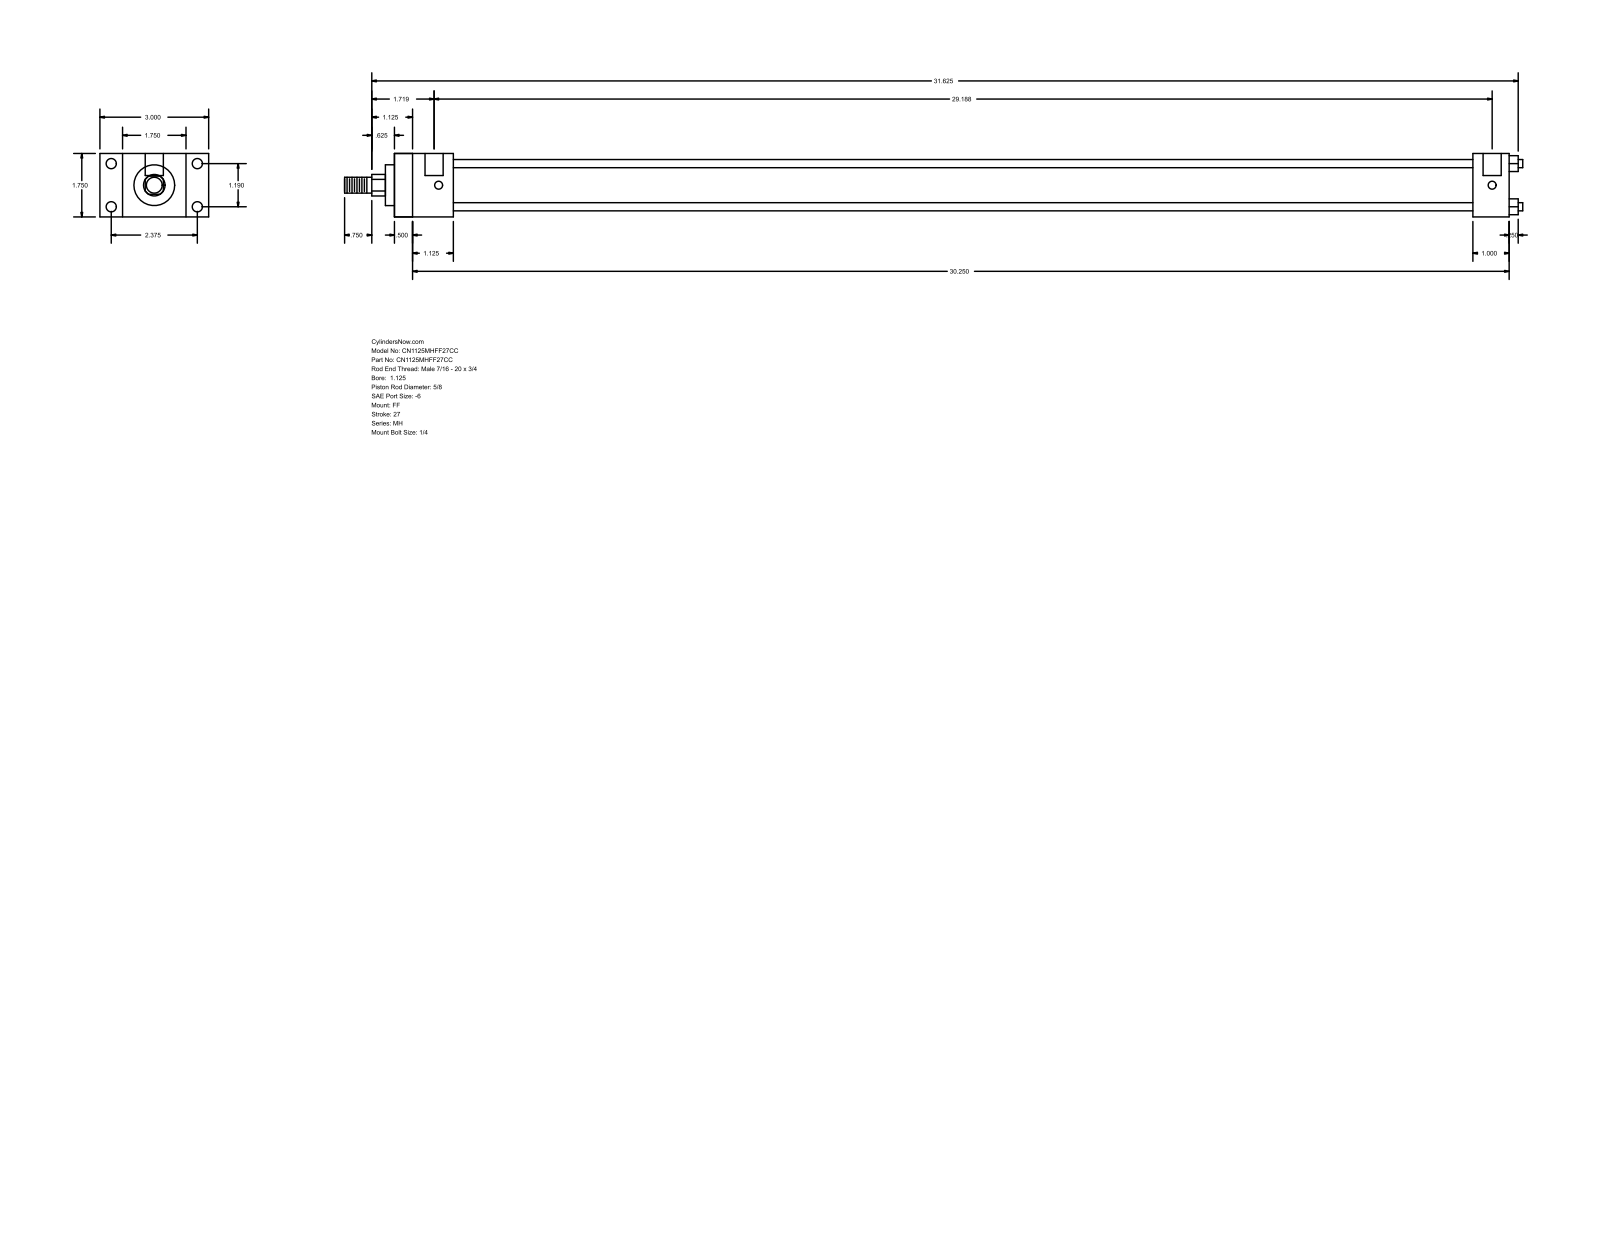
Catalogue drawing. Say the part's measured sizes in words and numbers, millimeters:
The part is named "MH_FF__0112_0.625". Its 3-D file was written by "GSSL Pune (CONFIG_CONTROL_DESIGN)". It is 0 solids with 92 faces: 64 planar, 28 cylindrical and 0 other. Overall it measures 825.5 by 76.2 by 44.45 millimeters. Round holes: 4 of diameter 5.56, 4 of diameter 7.14, 2 of diameter 12.7. Round bosses or shafts: 4 of diameter 5.71, 1 of diameter 34.92, 1 of diameter 28.57, 1 of diameter 15.88, 1 of diameter 11.11. Partial cylindrical surfaces (rounded edges, fillets, slot ends): 1 of radius 7.54. The main face-to-face distances are 44.46, 781.04, 12.69, 768.35, 15.87, 28.58, 60.33, 25.4, 41.27, 755.64. The hole center spacings are 30.22, 60.32, 67.47, 738.19, 3.17, 741.36.
